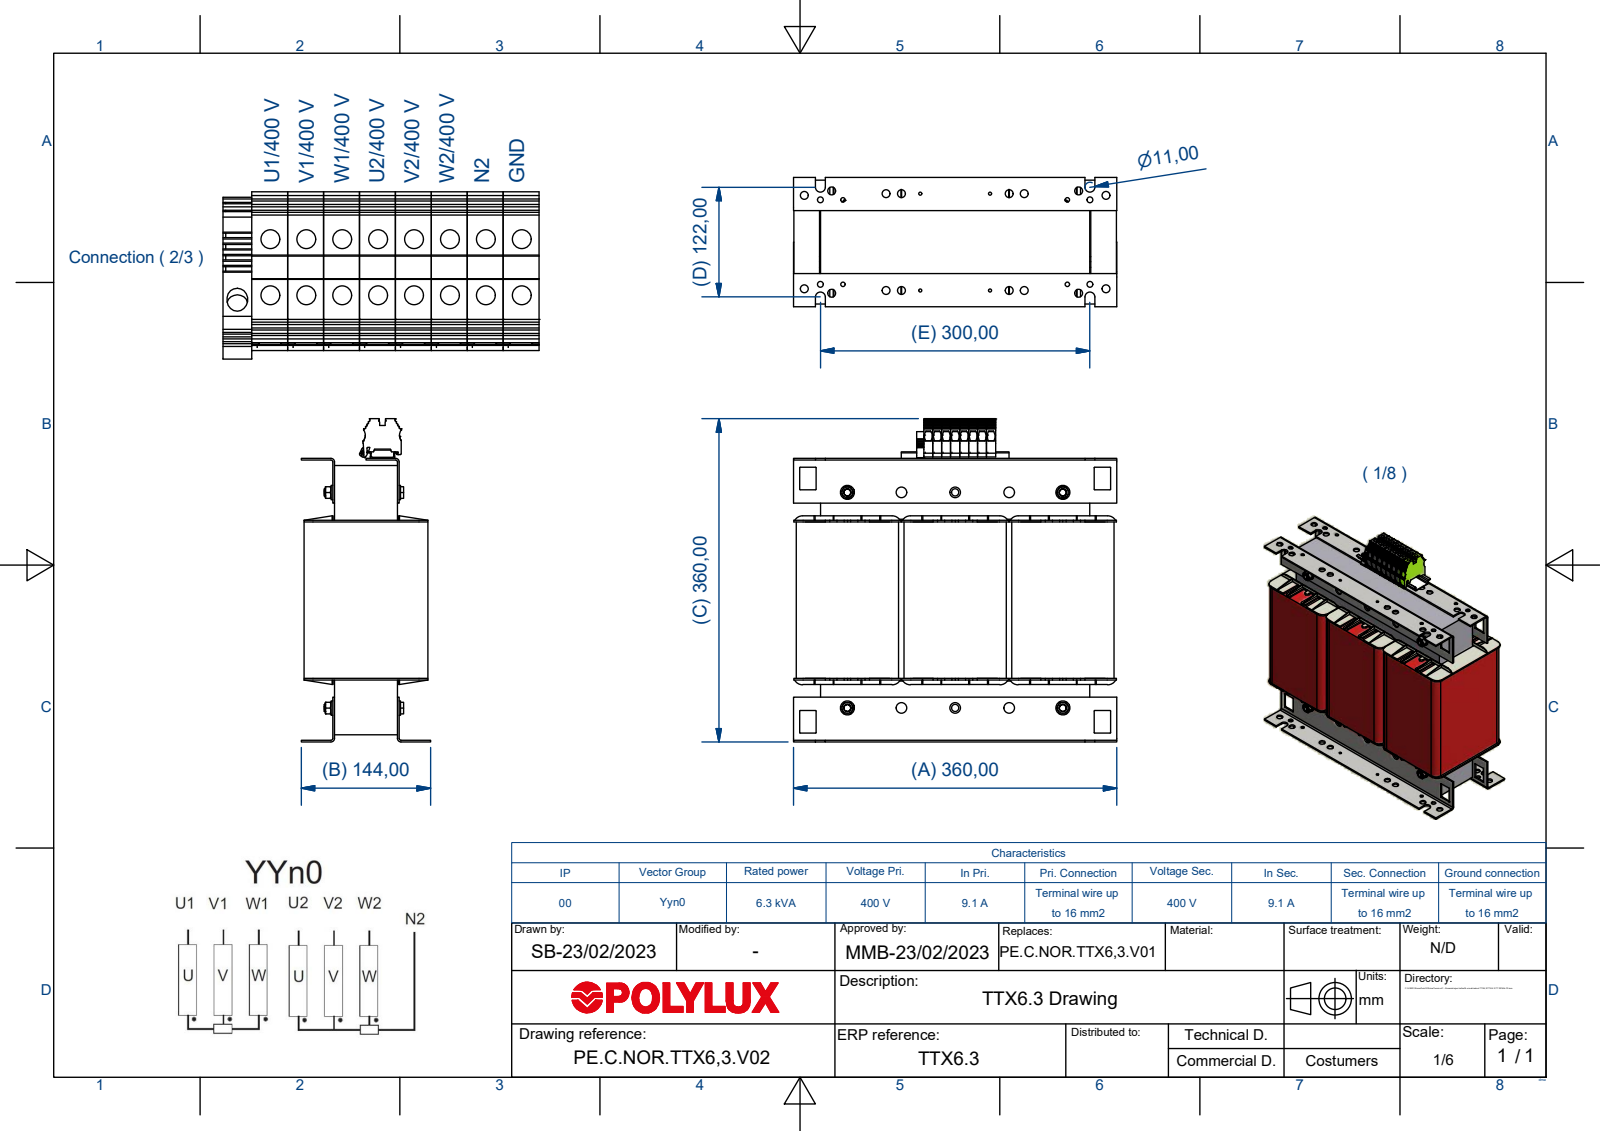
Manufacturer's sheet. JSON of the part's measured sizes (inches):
{"part_name": "TTX6.3; Núcleo RC60x70; BRI60-3IP0E25; TOR885E (+8 more)", "step_written_by": "Autodesk Inventor 2018 (AUTOMOTIVE_DESIGN)", "units": "inches", "bodies": {"solids": 38, "faces": 2746, "planar": 1936, "cylindrical": 786, "other": 24}, "overall_size": [14.178, 14.173, 5.669], "volume_in3": 676.8, "surface_area_in2": 2353, "round_holes": [[0.354, 28], [0.209, 16], [0.262, 10], [0.472, 10], [0.138, 6], [0.194, 6], [0.315, 6], [0.118, 2], [0.228, 2]], "round_bosses_or_shafts": [[0.63, 4]], "partial_cylinders_radius": [[0.02, 49], [0.394, 40], [0.157, 28], [0.433, 18], [0.079, 17], [0.039, 12], [0.012, 10], [0.004, 9]], "face_to_face_distances": [0.079, 0.039, 4.724, 2.874, 0.118, 9.449, 0.945, 3.543, 2.795, 1.26], "hole_center_spacings": [0.63, 2.362, 4.124, 4.724, 9.74, 9.449, 4.252, 10.564]}
